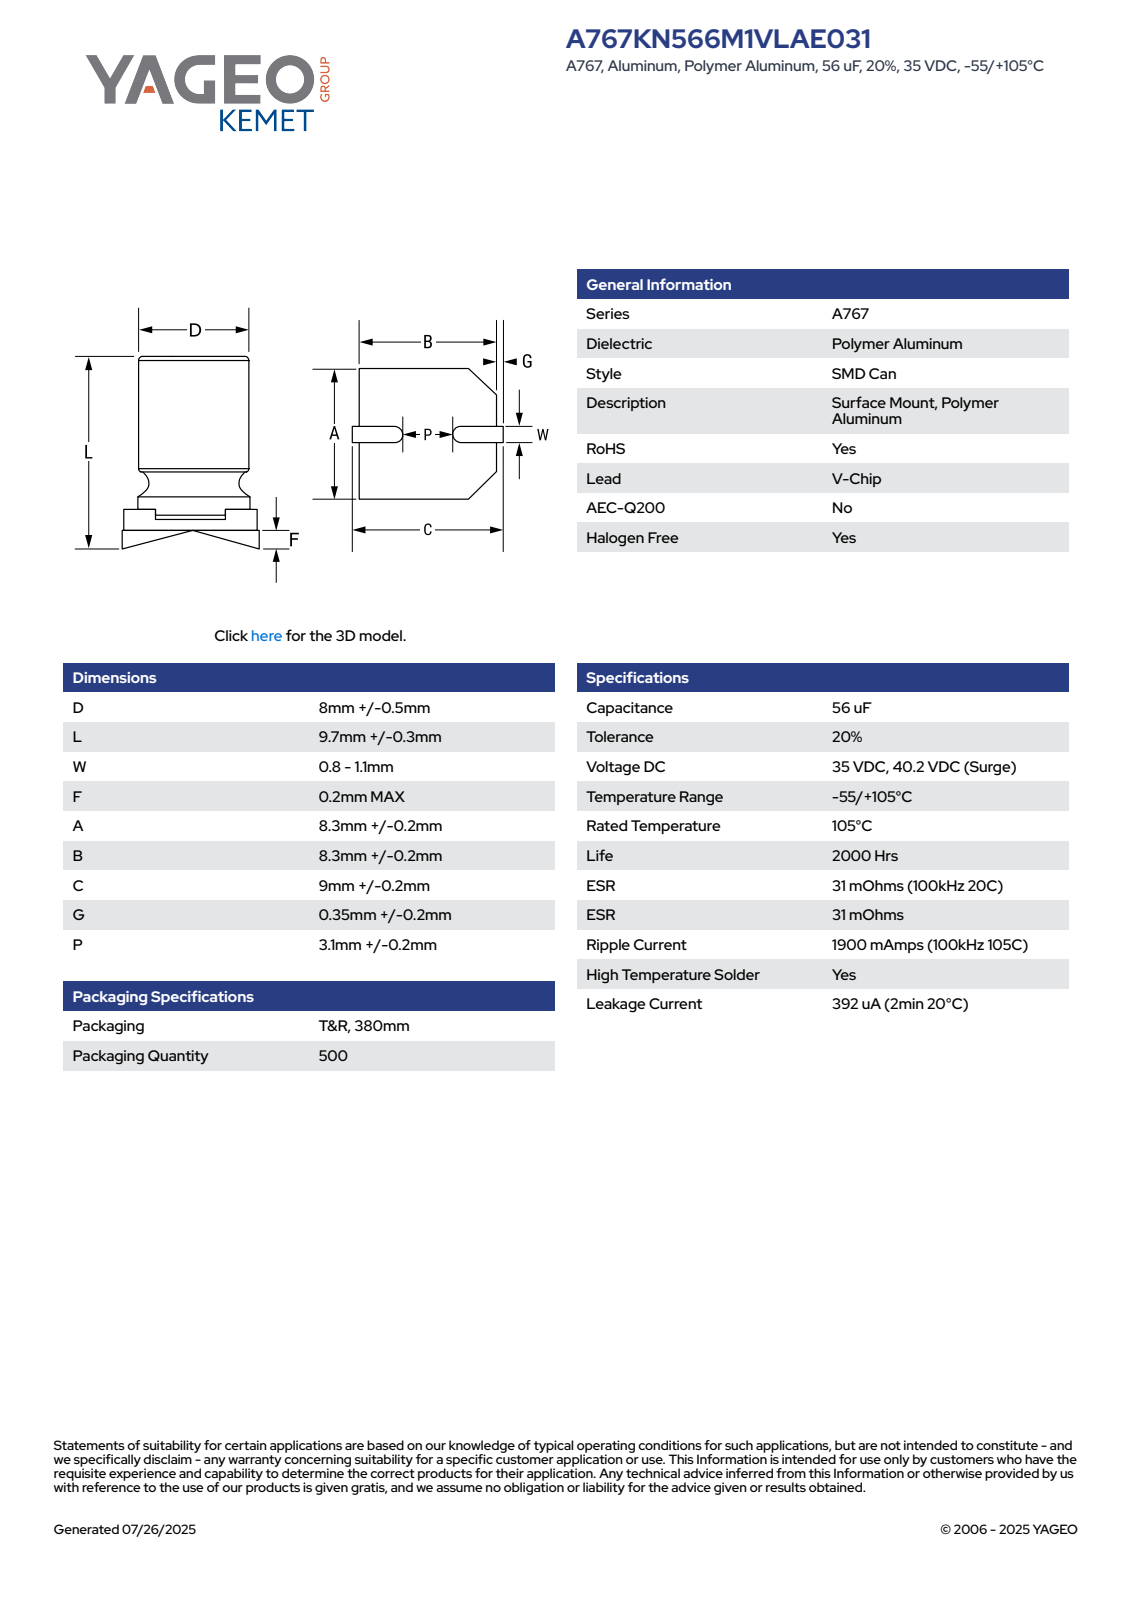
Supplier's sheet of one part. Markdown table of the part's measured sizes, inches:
| quantity | value |
| --- | --- |
| part name | CAC_KS_8X9.7_D8.5L10W1.1F0.2A8.5B8.5C9.2P3.3 |
| STEP written by | SolidWorks 2014 (AUTOMOTIVE_DESIGN) |
| units | inches |
| bodies | 5 solids, 76 faces (59 planar, 11 cylindrical, 6 other) |
| overall size | 0.394 × 0.362 × 0.335 |
| volume | 0.032 in³ |
| surface area | 0.876 in² |
| round bosses / shafts (diameter × count) | 0.32 × 1 |
| partial cylindrical surfaces (radius × count) | 0.008 × 2, 0.133 × 1, 0.167 × 1 |
| main face-to-face distances | 0.02, 0.386, 0.366, 0.386, 0.367, 0.335, 0.098, 0.079, 0.287, 0.288 |
